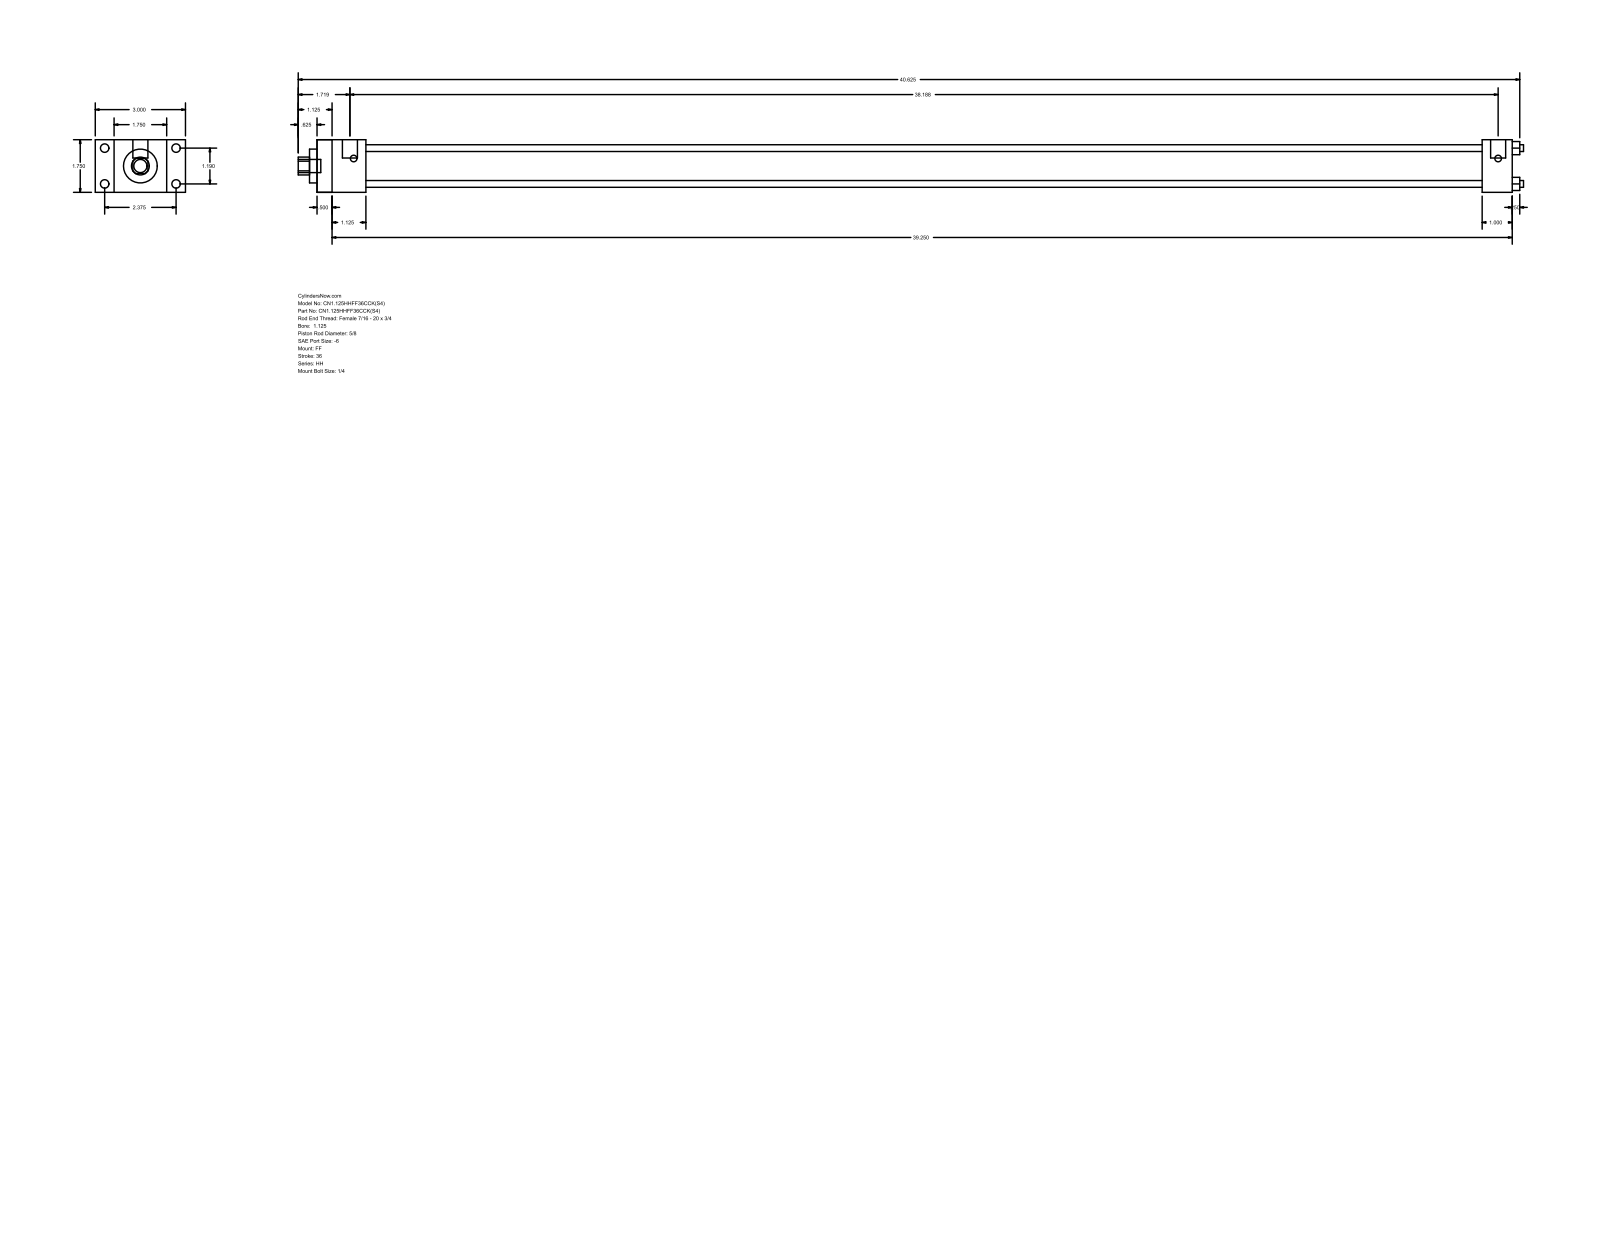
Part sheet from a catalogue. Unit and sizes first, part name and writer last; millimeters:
Units: millimetres
Overall size (bounding box): 1035.05 × 76.2 × 44.45
Round holes (diameter × count): ⌀5.71 ×4, ⌀15.88 ×1, ⌀28.57 ×1, ⌀34.92 ×1
Round bosses / shafts (diameter × count): ⌀7.14 ×4, ⌀5.56 ×4, ⌀12.7 ×2, ⌀11.11 ×1
Partial cylindrical surfaces — rounded edges, fillets, slot ends (radius × count): R7.54 ×1
Main face-to-face distances: 44.46, 1009.65, 12.69, 996.96, 15.87, 60.33, 28.58, 41.27, 984.24, 971.55
Hole centre spacings: 21.37, 30.22, 42.74
Bodies: 0 solids, 92 faces (64 planar, 28 cylindrical, 0 other)
Part name (STEP PRODUCT): HH_FF__0112_0.625
STEP written by: GSSL Pune (CONFIG_CONTROL_DESIGN)
